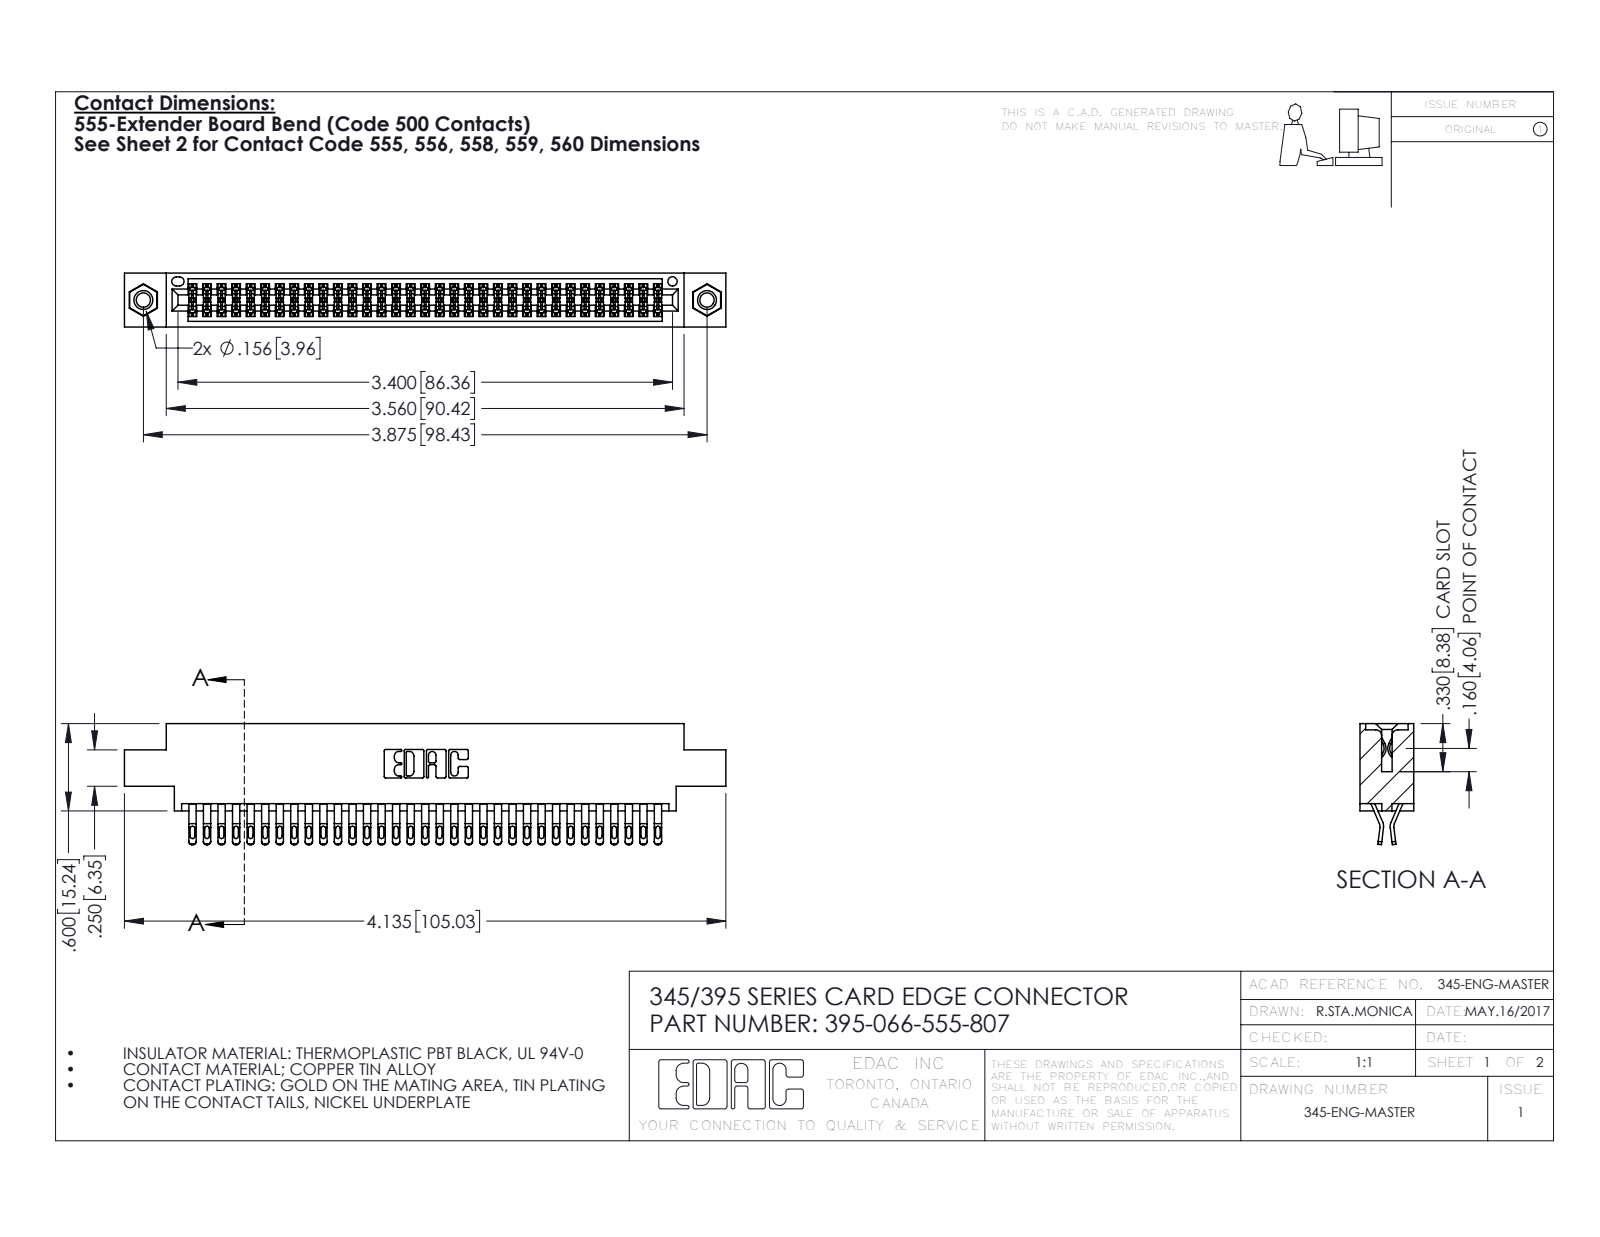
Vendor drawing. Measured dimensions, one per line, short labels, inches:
name: 345 Part_0.170 Offset - 0.156 Dia-TI; 345-250-001_345-250-005-103; 395-066-555-807; 345-292-001_555 Tail
written by: SolidWorks 2016 (CONFIG_CONTROL_DESIGN)
unit: in
bodies: 69 solids, 3886 faces (2162 planar, 1708 cylindrical, 16 other)
size: 4.135 × 0.832 × 0.37
volume: 0.621 in³; area: 24.36 in²
holes: 2× ⌀0.098, 2× ⌀0.125, 2× ⌀0.156, 1× ⌀0.064
bosses: 2× ⌀0.155
rounds: 165× R0.016, 132× R0.02, 99× R0.006, 22× R0.01, 6× R0.007, 6× R0.031, 3× R0.026, 2× R0.01
face distances: 0.072, 0.298, 0.37, 0.025, 0.2, 0.098, 0.272, 0.225, 0.175, 0.149
hole spacings: 0.27, 3.64, 3.875
